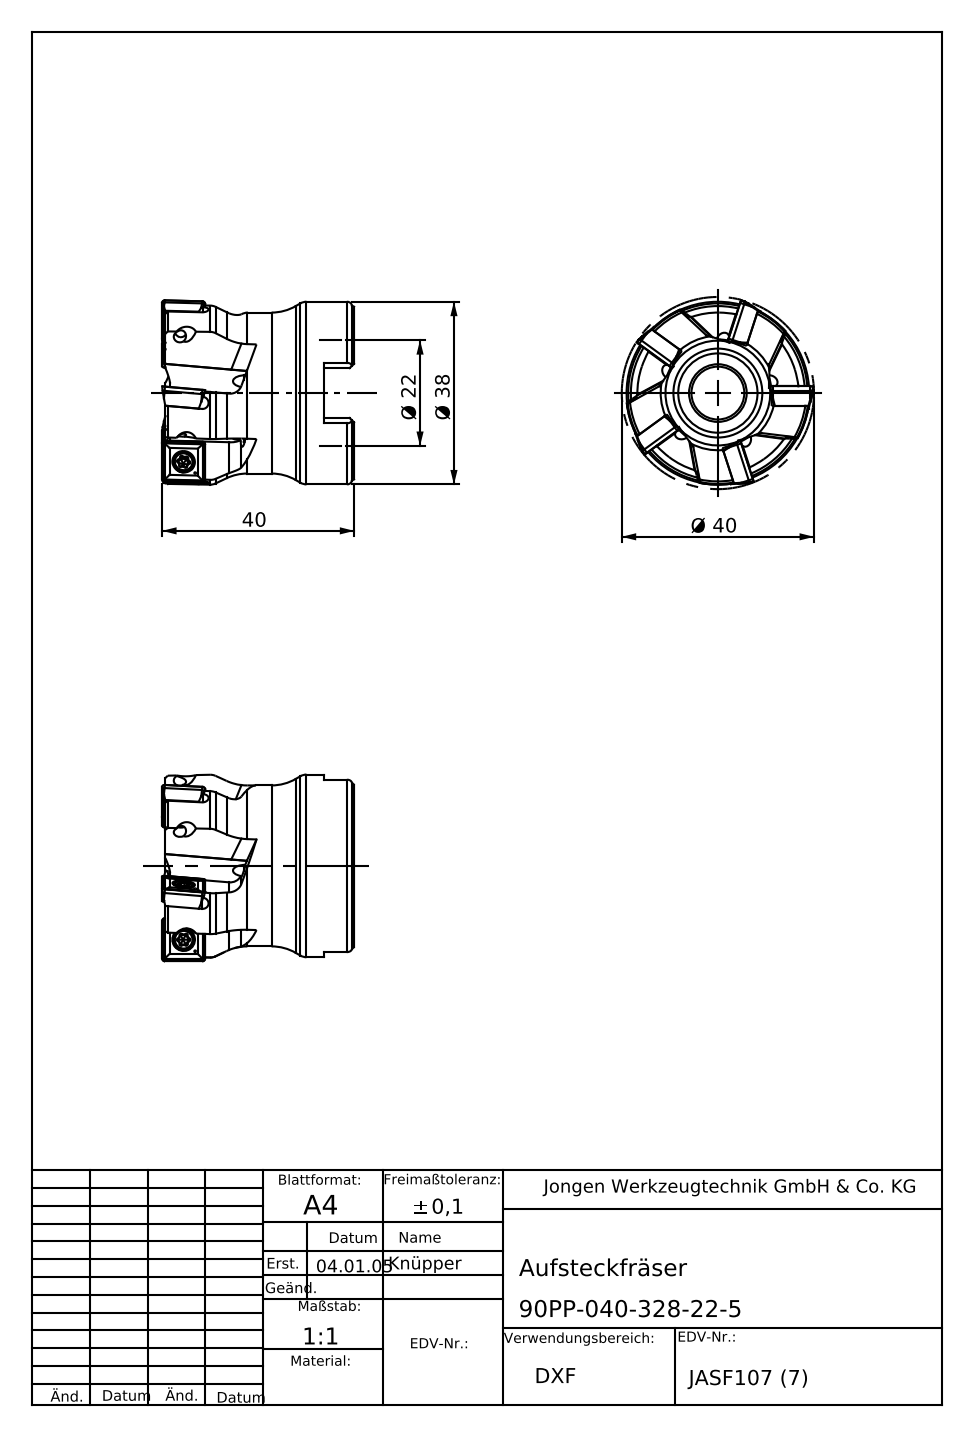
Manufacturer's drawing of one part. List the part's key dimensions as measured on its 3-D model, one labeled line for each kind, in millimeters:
Part name (STEP PRODUCT): 90PP-040-328-22-5
STEP written by: SolidWorks 2013 (AUTOMOTIVE_DESIGN)
Units: millimetres
Bodies: 1 solid, 201 faces (88 planar, 49 cylindrical, 64 other)
Overall size (bounding box): 40 × 39.98 × 39.98
Volume: 27 011 mm³ · Surface area: 10 361 mm²
Round holes (diameter × count): ⌀2.5 ×5, ⌀11 ×1, ⌀16.5 ×1, ⌀22 ×1, ⌀22.15 ×1, ⌀22.3 ×1
Round bosses / shafts (diameter × count): ⌀38 ×1, ⌀33.5 ×1
Partial cylindrical surfaces — rounded edges, fillets, slot ends (radius × count): R1.25 ×10, R2.5 ×5
Main face-to-face distances: 23, 6.3, 16.7, 38.3, 32, 15.3, 28.3, 22, 5.3, 10
